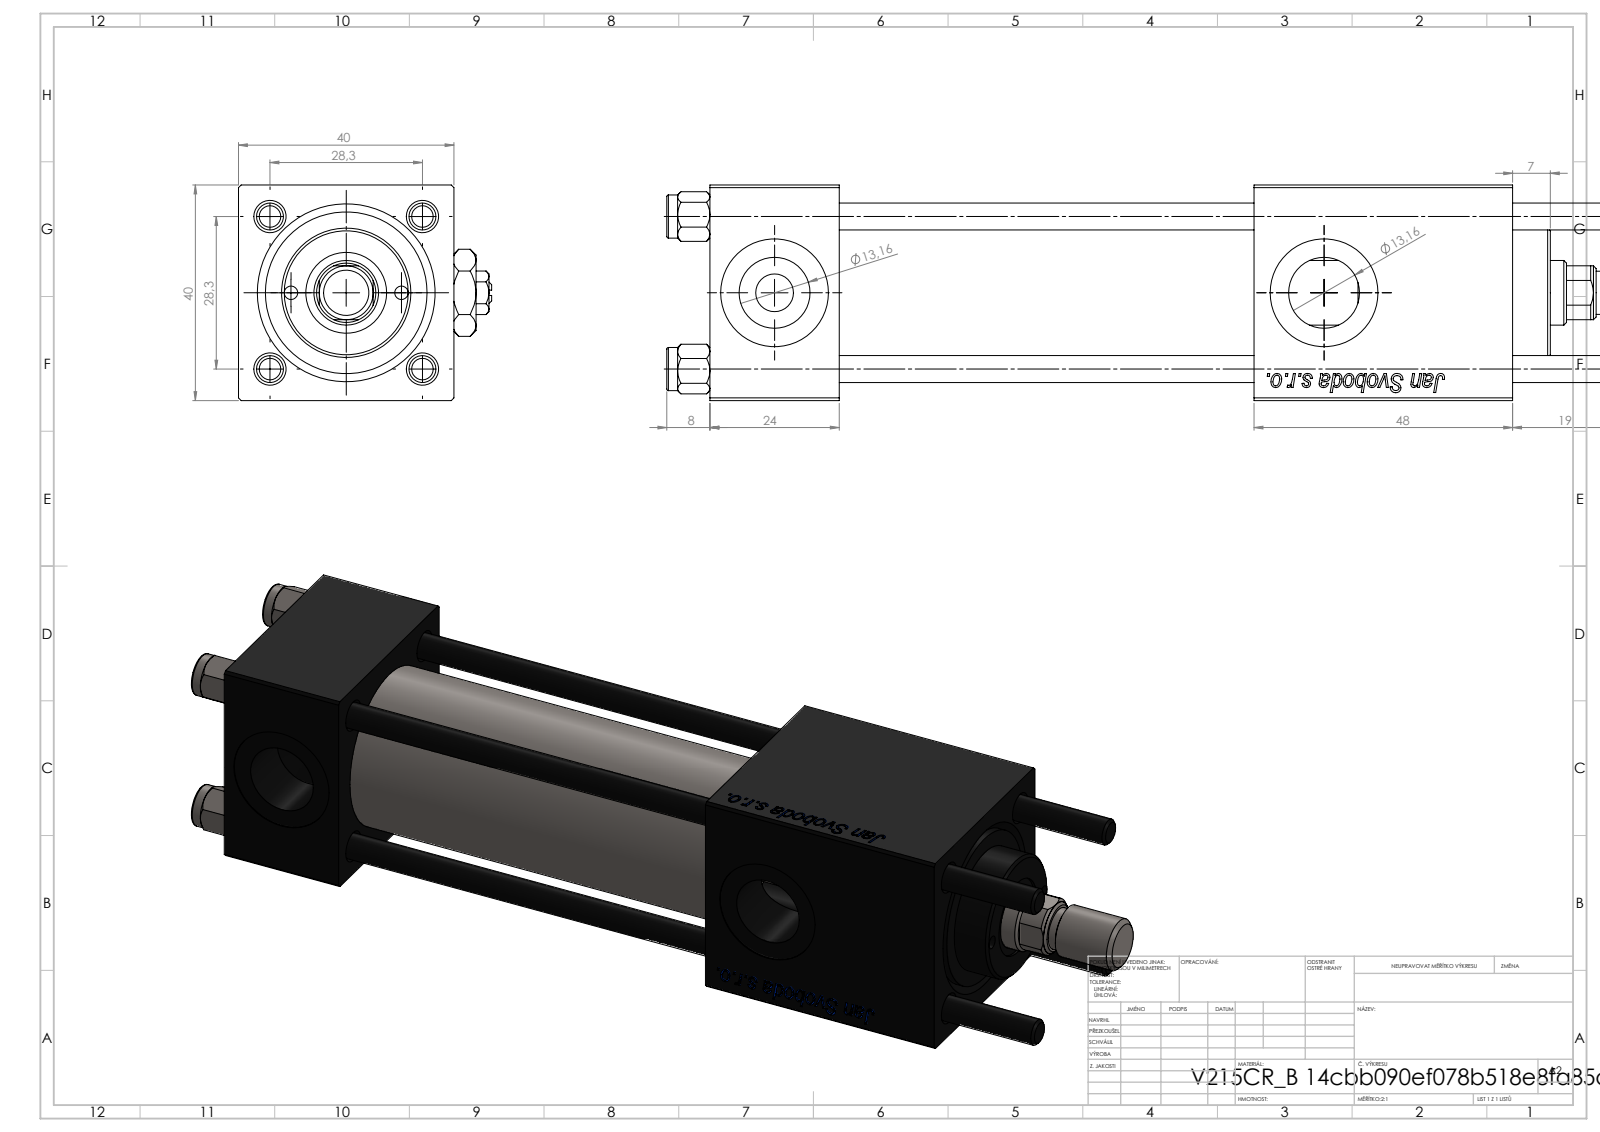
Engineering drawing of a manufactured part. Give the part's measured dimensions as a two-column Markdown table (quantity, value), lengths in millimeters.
| quantity | value |
| --- | --- |
| part name | NUT_M5_B; V215CR_VCP_B; ROD_END_AH; V215CR_B_TYCINKA (+3 more) |
| STEP written by | SolidWorks 2019 (CONFIG_CONTROL_DESIGN) |
| units | millimeters |
| bodies | 13 solids, 1228 faces (458 planar, 94 cylindrical, 676 other) |
| overall size | 186 × 47 × 40 |
| volume | 158 710 mm³ |
| surface area | 68 736 mm² |
| round holes (diameter × count) | 5 × 4, 20 × 3, 2.5 × 2, 7 × 2, 13.16 × 2, 6.5 × 1, 12 × 1, 15 × 1, 25 × 1, 30 × 1 |
| round bosses / shafts (diameter × count) | 8 × 5, 31 × 1, 24 × 1, 10 × 1 |
| partial cylindrical surfaces (radius × count) | 5.5 × 1 |
| main face-to-face distances | 40, 24, 120.3, 96.3, 77, 149, 101, 19.3, 125, 48 |
| hole center spacings | 14.68, 20.01, 28.21, 28.3, 10.25, 40.02, 20.5, 102 |
